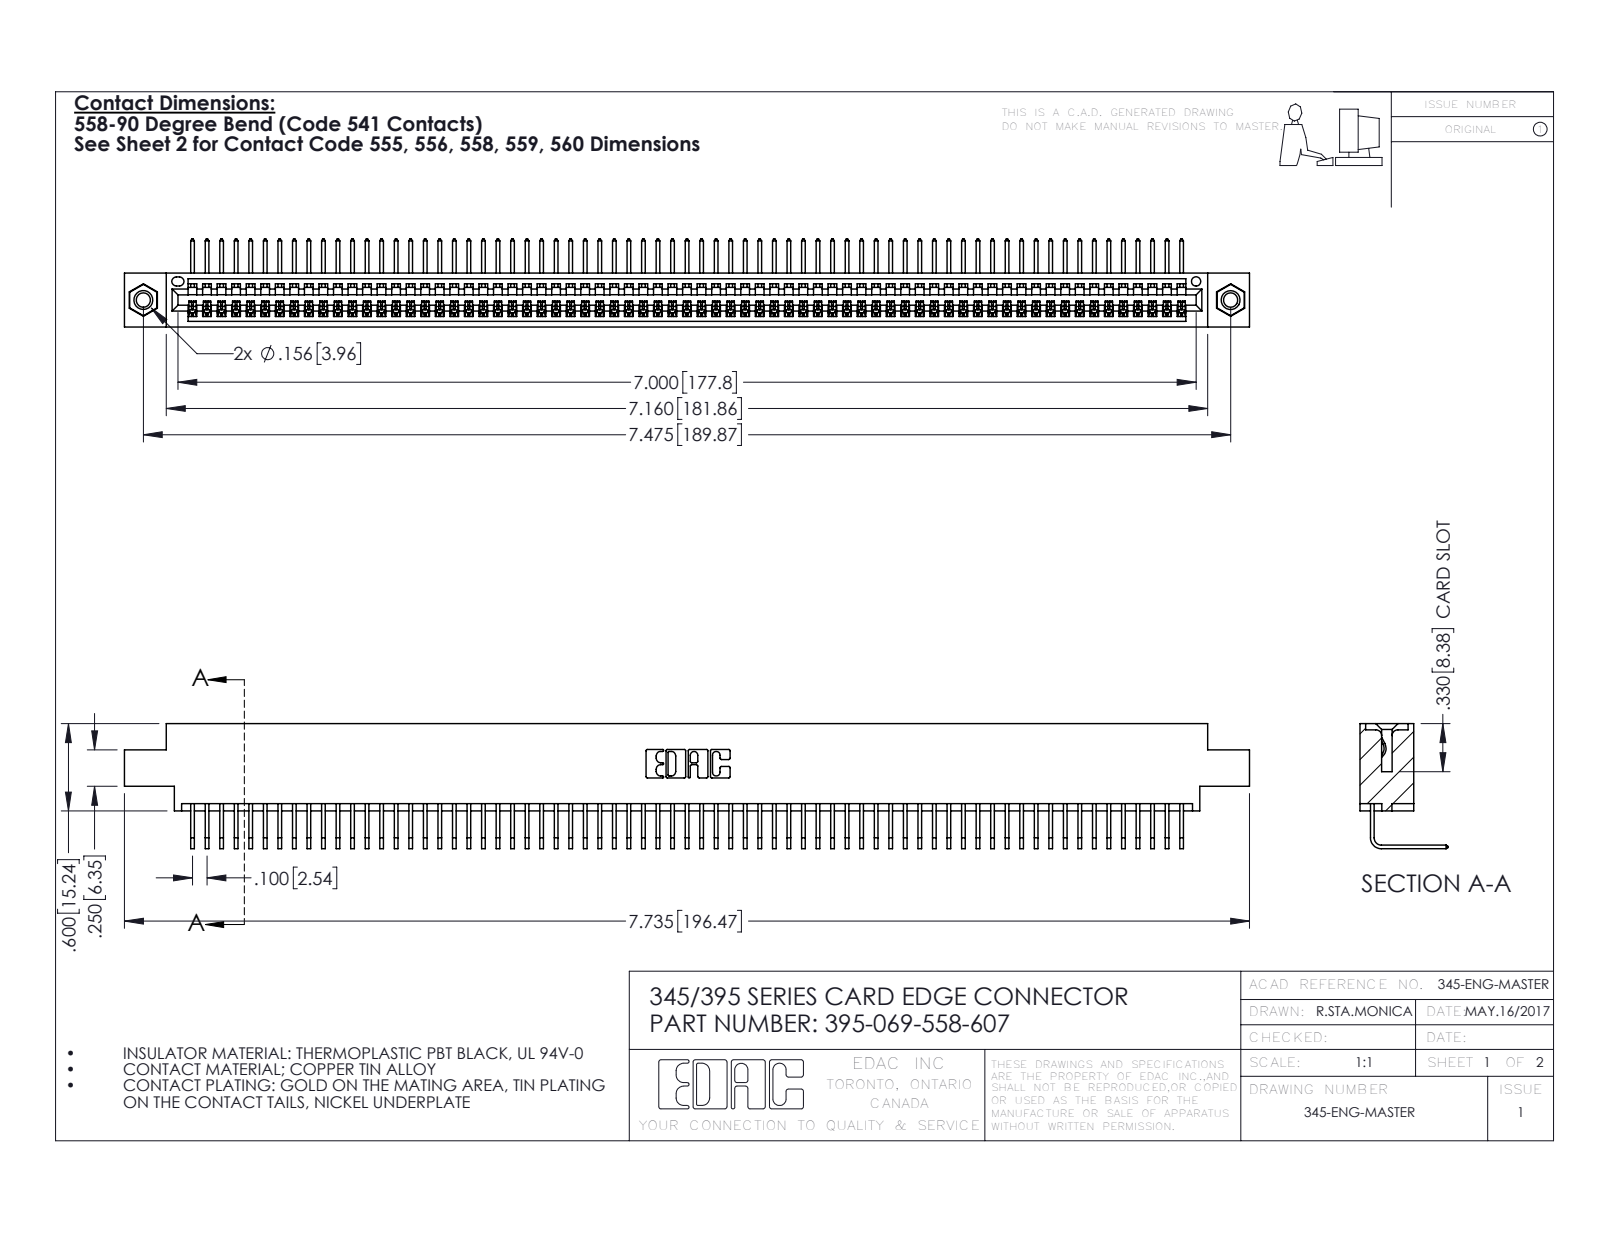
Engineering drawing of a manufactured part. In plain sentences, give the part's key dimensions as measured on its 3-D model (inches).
The part is named "345 Part_0.170 Offset - 0.156 Dia-TI; 345-292-001_558 Tail - 2; 395-069-558-607; 345-250-001_345-250-005-103". Its 3-D file was written by "SolidWorks 2016 (CONFIG_CONTROL_DESIGN)". It is 72 solids with 4330 faces: 3014 planar, 1300 cylindrical and 16 other. Overall it measures 7.735 by 0.859 by 0.605 inches. Its volume is 1.159 cubic inches and its surface area 42.01 square inches. Round holes: 2 of diameter 0.098, 2 of diameter 0.125, 2 of diameter 0.156, 1 of diameter 0.064. Round bosses or shafts: 2 of diameter 0.155. Partial cylindrical surfaces (rounded edges, fillets, slot ends): 138 of radius 0.006, 22 of radius 0.01, 6 of radius 0.007, 6 of radius 0.031, 3 of radius 0.026, 2 of radius 0.031, 2 of radius 0.04, 1 of radius 0.014. The main face-to-face distances are 0.072, 0.298, 0.37, 0.2, 0.098, 0.272, 0.025, 0.225, 0.175, 0.149. The hole center spacings are 0.27, 7.239, 7.475.
